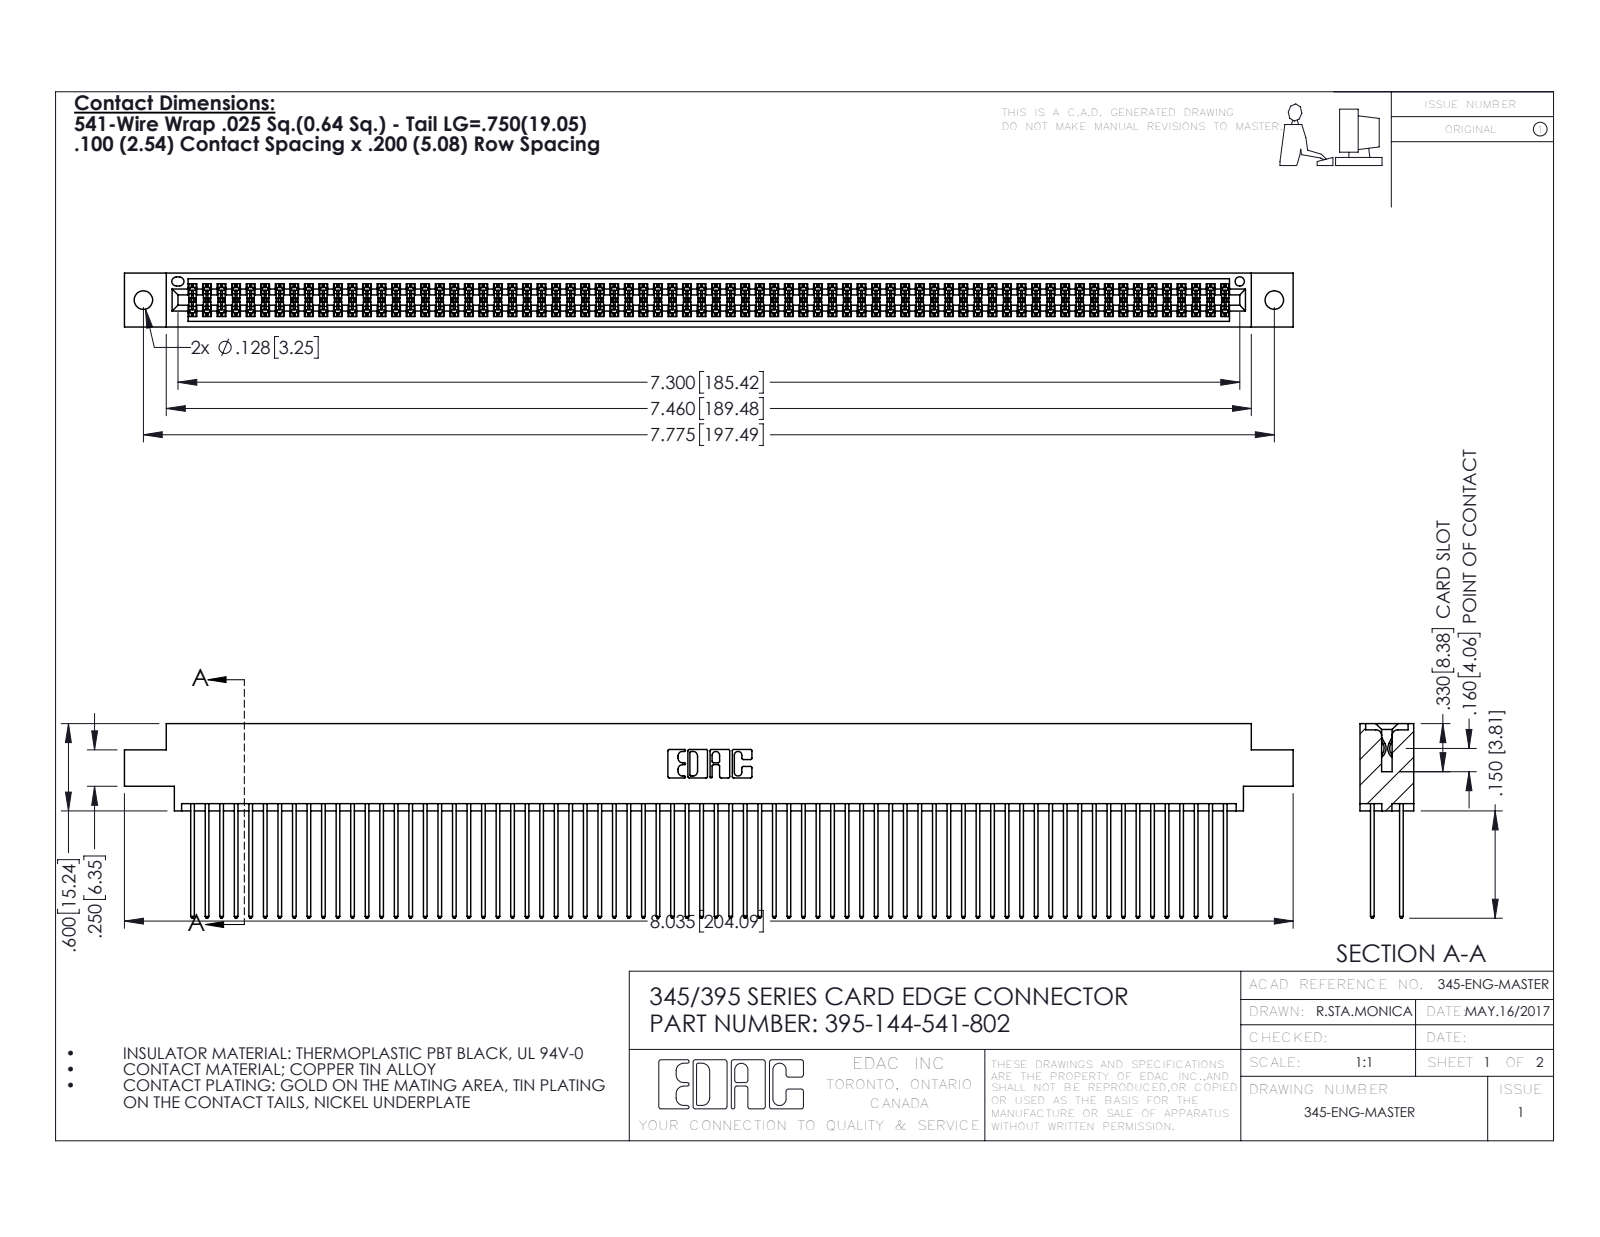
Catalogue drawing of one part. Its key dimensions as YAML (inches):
part_name: "395-144-541-802; 345 Part_0.170 Offset - 0.128 Dia; 345-292-001_345-293-141"
step_written_by: "SolidWorks 2016 (CONFIG_CONTROL_DESIGN)"
units: inches
bodies: {solids: 145, faces: 7330, planar: 4836, cylindrical: 2494, other: 0}
overall_size: [8.035, 1.337, 0.37]
volume: 1.268
surface_area: 54.33
round_holes:
  - {diameter: 0.128, count: 2}
  - {diameter: 0.064, count: 1}
partial_cylinders:
  - {radius: 0.006, count: 216}
  - {radius: 0.01, count: 144}
  - {radius: 0.01, count: 22}
  - {radius: 0.007, count: 6}
  - {radius: 0.031, count: 6}
  - {radius: 0.026, count: 3}
  - {radius: 0.014, count: 2}
  - {radius: 0.019, count: 2}
face_to_face_distances: [0.072, 0.298, 0.2, 0.098, 0.272, 0.025, 0.225, 0.37, 0.175, 0.149]
hole_center_spacings: [0.27, 7.539, 7.775]
